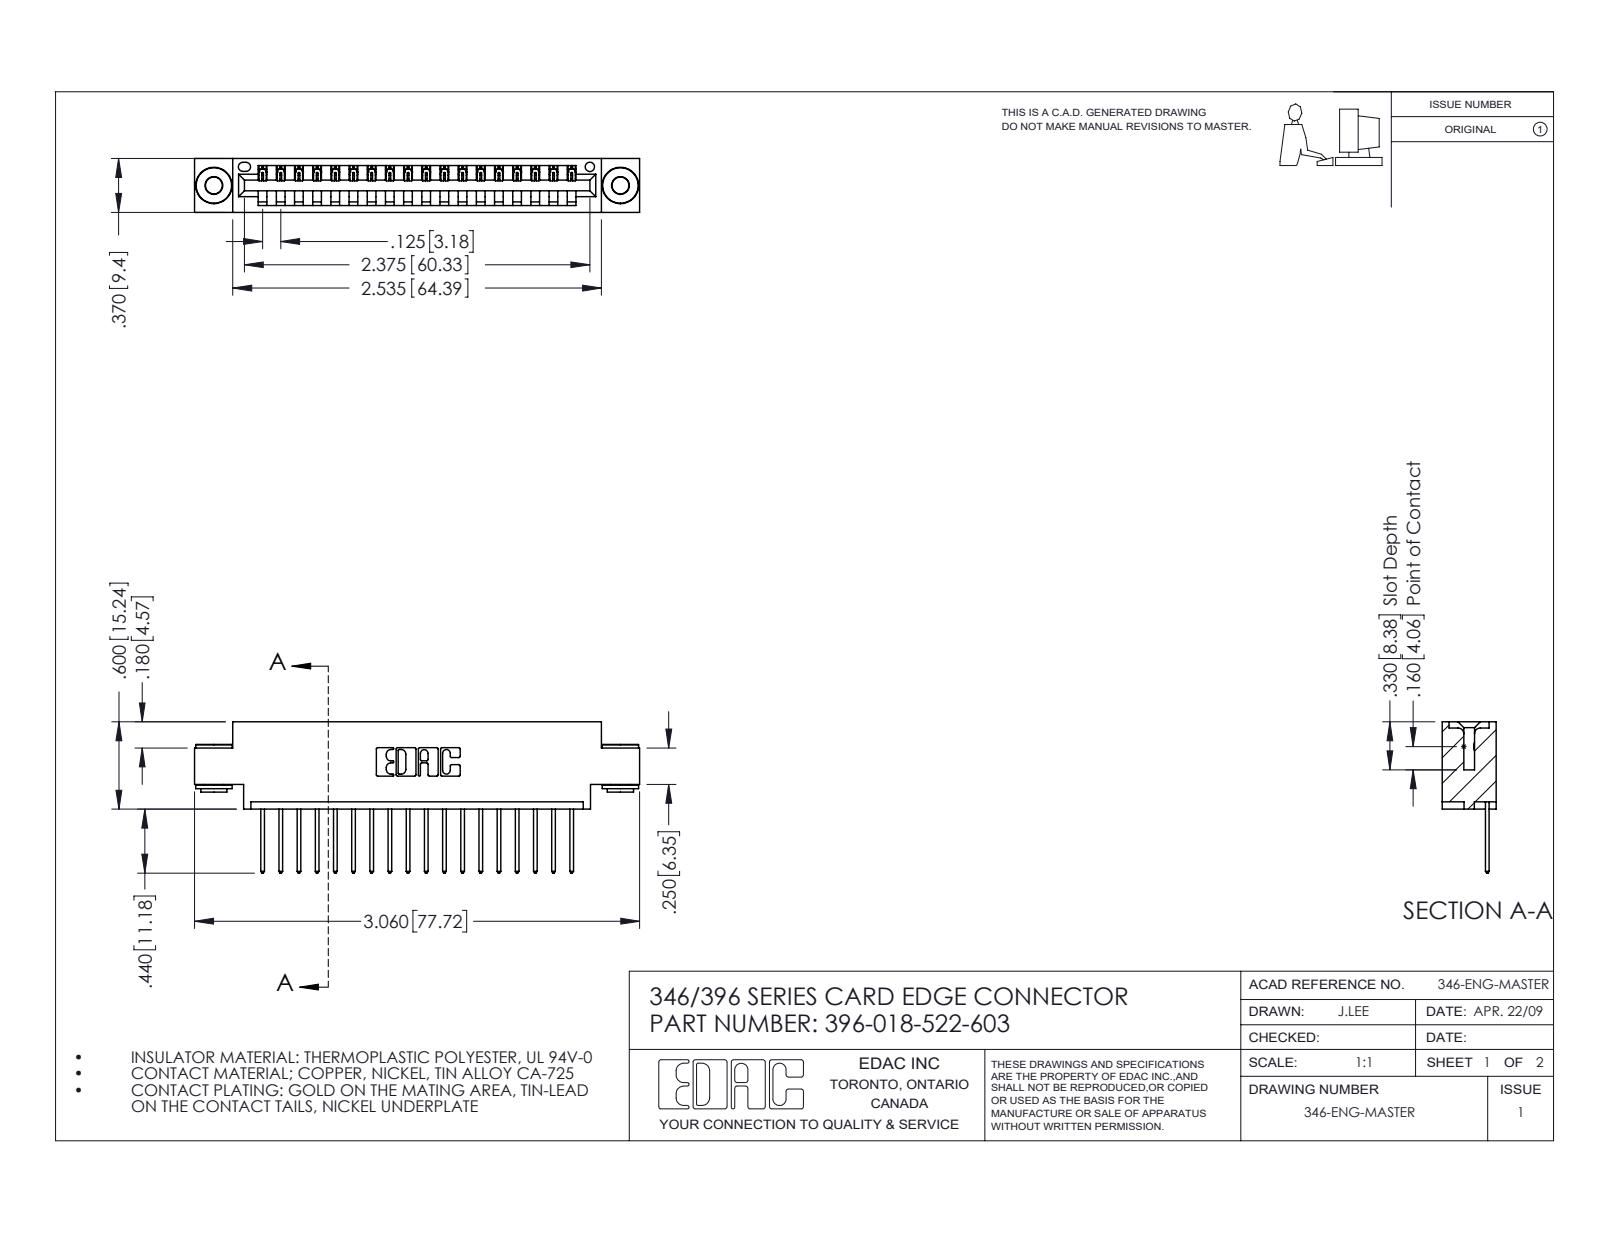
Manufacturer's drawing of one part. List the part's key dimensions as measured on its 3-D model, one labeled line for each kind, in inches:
Part name (STEP PRODUCT): 345-292-001_345-293-122; 396-018-522-603; 345-250-002_345-250-002-102; 346 Part_0.170 Offset - 0.156 Dia-TH
STEP written by: SolidWorks 2016 (CONFIG_CONTROL_DESIGN)
Units: inches
Bodies: 21 solids, 1208 faces (810 planar, 390 cylindrical, 8 other)
Overall size (bounding box): 3.06 × 1.04 × 0.37
Volume: 0.436 in³ · Surface area: 14.12 in²
Round holes (diameter × count): ⌀0.116 ×2, ⌀0.156 ×2, ⌀0.064 ×1
Round bosses / shafts (diameter × count): ⌀0.25 ×2, ⌀0.18 ×2, ⌀0.136 ×2
Partial cylindrical surfaces — rounded edges, fillets, slot ends (radius × count): R0.006 ×36, R0.01 ×36, R0.01 ×22, R0.007 ×6, R0.031 ×6, R0.026 ×3, R0.031 ×2, R0.04 ×2
Main face-to-face distances: 0.048, 0.322, 0.37, 0.25, 0.025, 0.072, 0.298, 0.148, 0.222, 0.1
Hole centre spacings: 0.246, 2.588, 2.795
